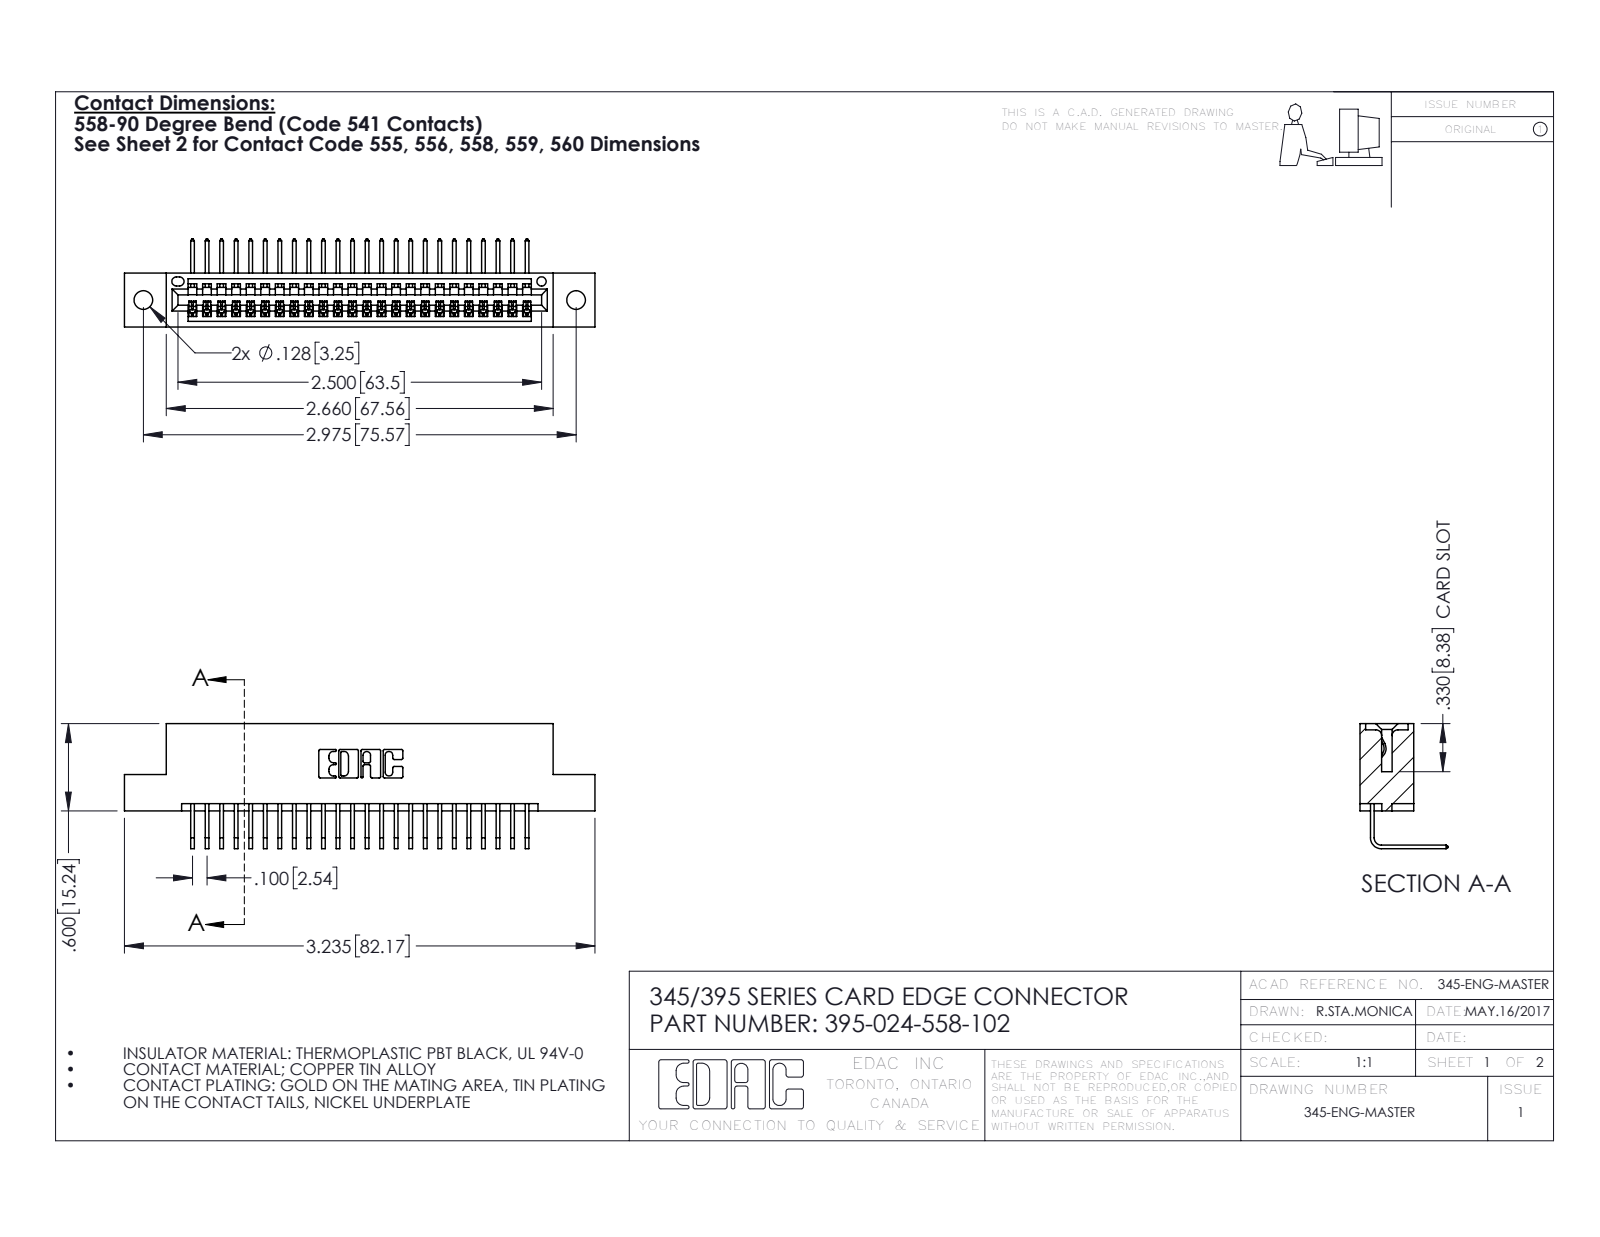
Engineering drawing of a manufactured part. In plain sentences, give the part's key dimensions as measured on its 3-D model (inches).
The part is named "345-292-001_558 Tail - 2; 345 Part_Flush Mounting Lugs - 0.128 Dia; 395-024-558-102". Its 3-D file was written by "SolidWorks 2016 (CONFIG_CONTROL_DESIGN)". It is 25 solids with 1566 faces: 1088 planar, 478 cylindrical and 0 other. Overall it measures 3.235 by 0.859 by 0.605 inches. Its volume is 0.47 cubic inches and its surface area 15.79 square inches. Round holes: 2 of diameter 0.128, 1 of diameter 0.064. Partial cylindrical surfaces (rounded edges, fillets, slot ends): 48 of radius 0.006, 22 of radius 0.01, 6 of radius 0.007, 6 of radius 0.031, 3 of radius 0.026, 2 of radius 0.031, 2 of radius 0.04, 1 of radius 0.014. The main face-to-face distances are 0.298, 0.072, 0.2, 0.37, 0.098, 0.272, 0.025, 0.225, 0.149, 0.072. The hole center spacings are 0.27, 2.741, 2.975.
